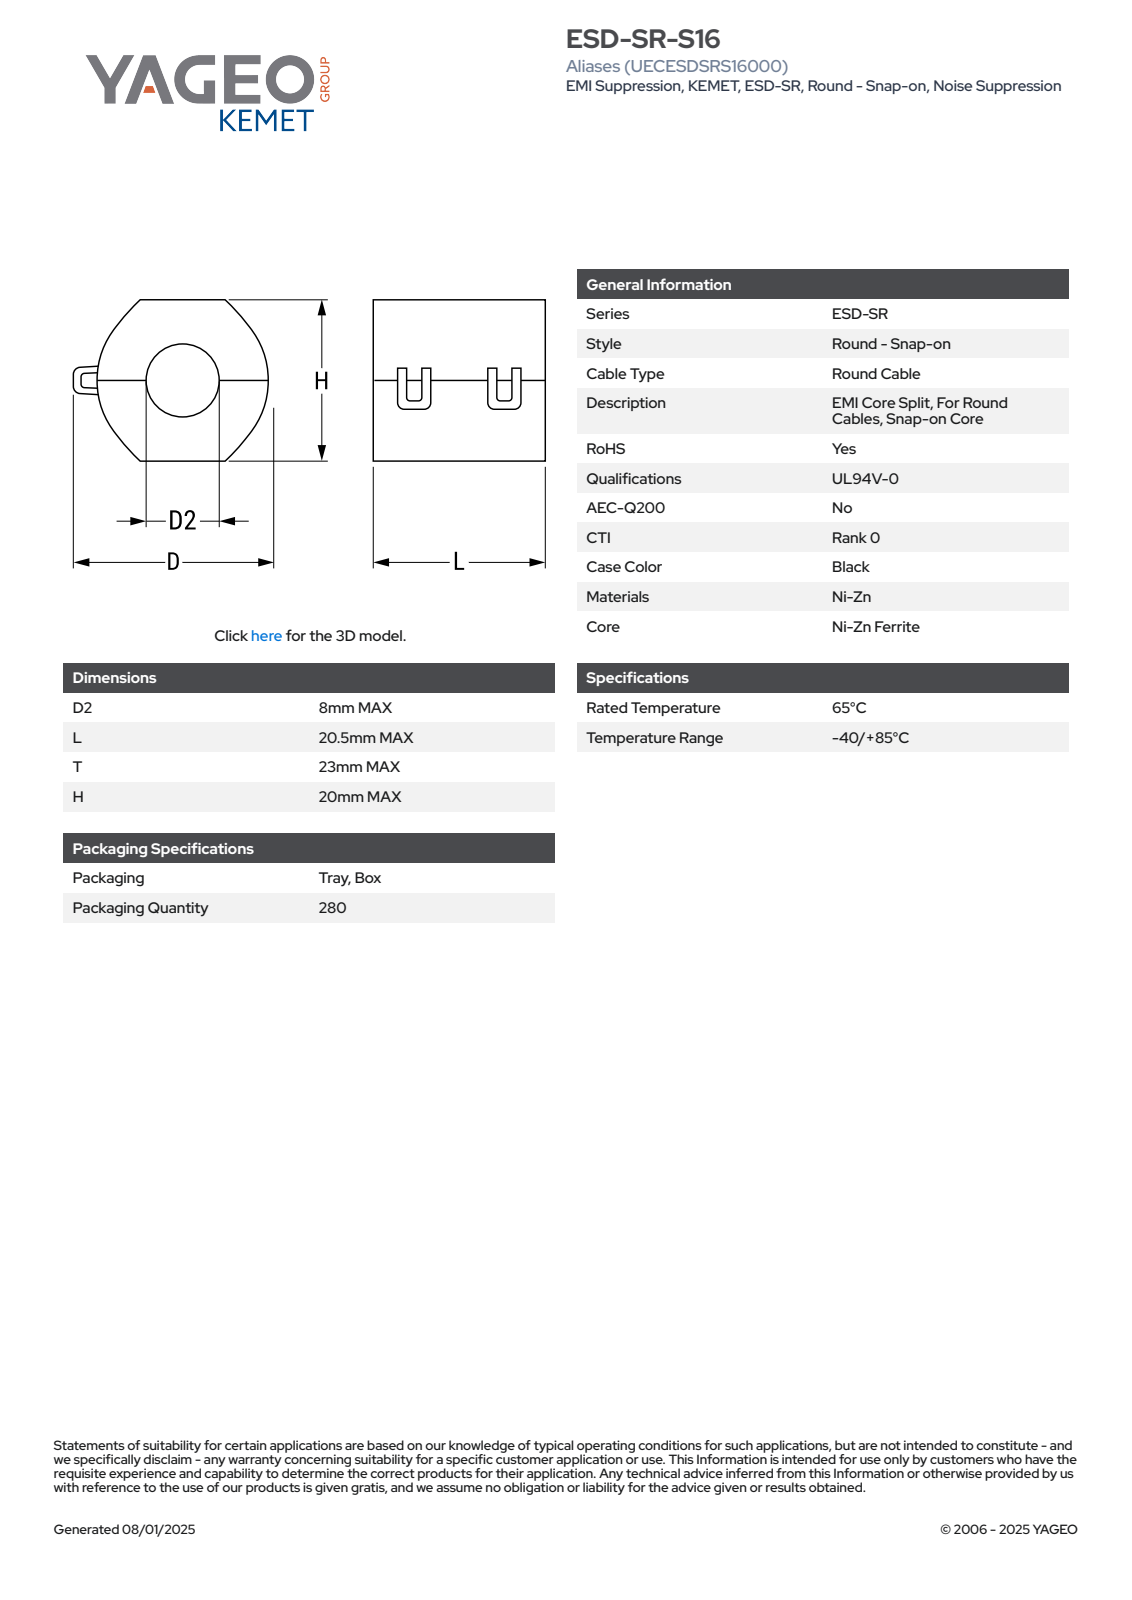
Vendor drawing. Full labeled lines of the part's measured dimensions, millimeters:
Part name (STEP PRODUCT): EC_ESDSRS_D28L20.5T23H20
STEP written by: SolidWorks 2014 (AUTOMOTIVE_DESIGN)
Units: millimetres
Bodies: 2 solids, 84 faces (78 planar, 6 cylindrical, 0 other)
Overall size (bounding box): 23 × 20.5 × 20
Volume: 6 766 mm³ · Surface area: 3 234 mm²
Round holes (diameter × count): ⌀8 ×1
Partial cylindrical surfaces — rounded edges, fillets, slot ends (radius × count): R11.25 ×1
Main face-to-face distances: 9.99, 10.01, 20.5, 20, 0.52, 4.37, 8.37, 12.13, 16.13, 4
